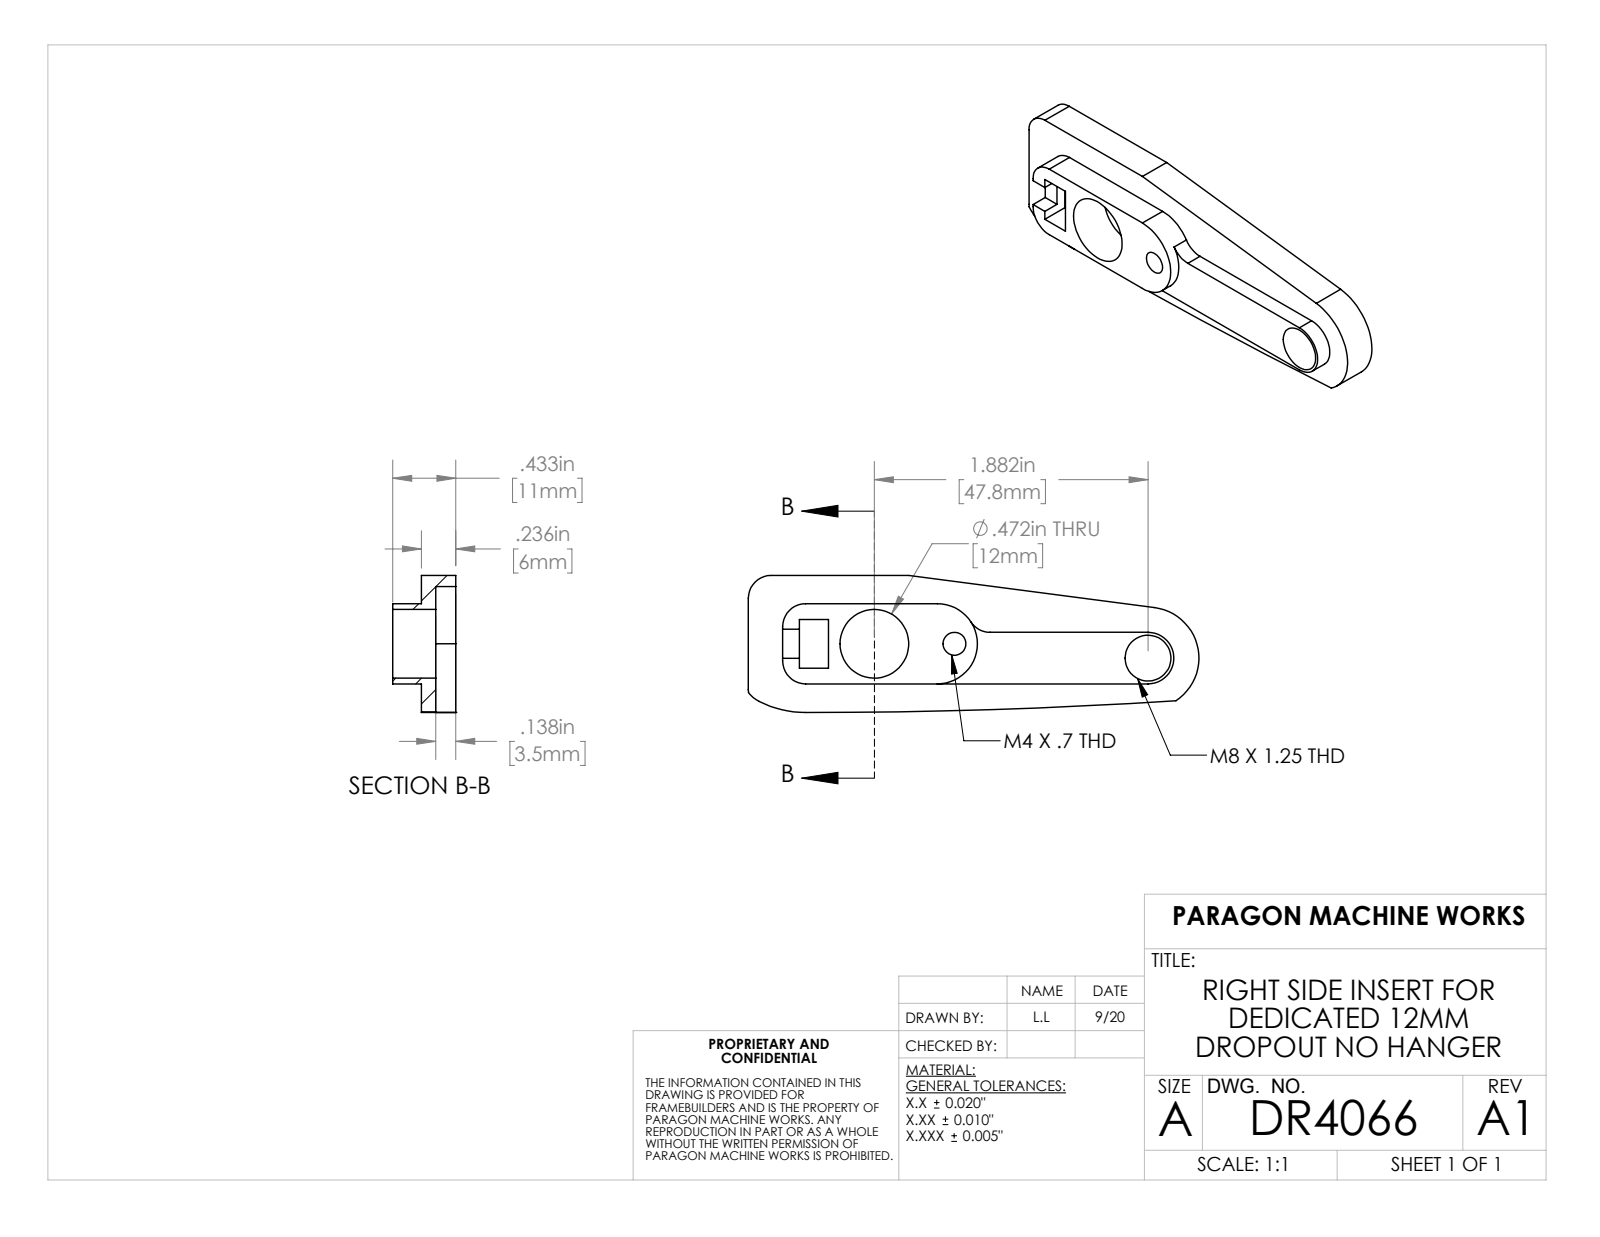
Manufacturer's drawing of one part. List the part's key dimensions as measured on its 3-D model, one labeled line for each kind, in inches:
Part name (STEP PRODUCT): DR4066
STEP written by: SolidWorks 2020 (AUTOMOTIVE_DESIGN)
Units: inches
Bodies: 1 solid, 45 faces (24 planar, 21 cylindrical, 0 other)
Overall size (bounding box): 3.098 × 0.942 × 0.433
Volume: 0.604 in³ · Surface area: 8.543 in²
Round holes (diameter × count): ⌀0.157 ×1, ⌀0.315 ×1, ⌀0.472 ×1
Partial cylindrical surfaces — rounded edges, fillets, slot ends (radius × count): R0.157 ×5, R0.394 ×2, R0.177 ×1, R0.206 ×1, R0.276 ×1, R0.35 ×1, R0.705 ×1, R40 ×1
Main face-to-face distances: 0.236, 0.197, 0.354, 0.079, 0.118, 0.098, 0.138, 0.295, 0.433, 0.217
Hole centre spacings: 0.551, 1.334, 1.884
